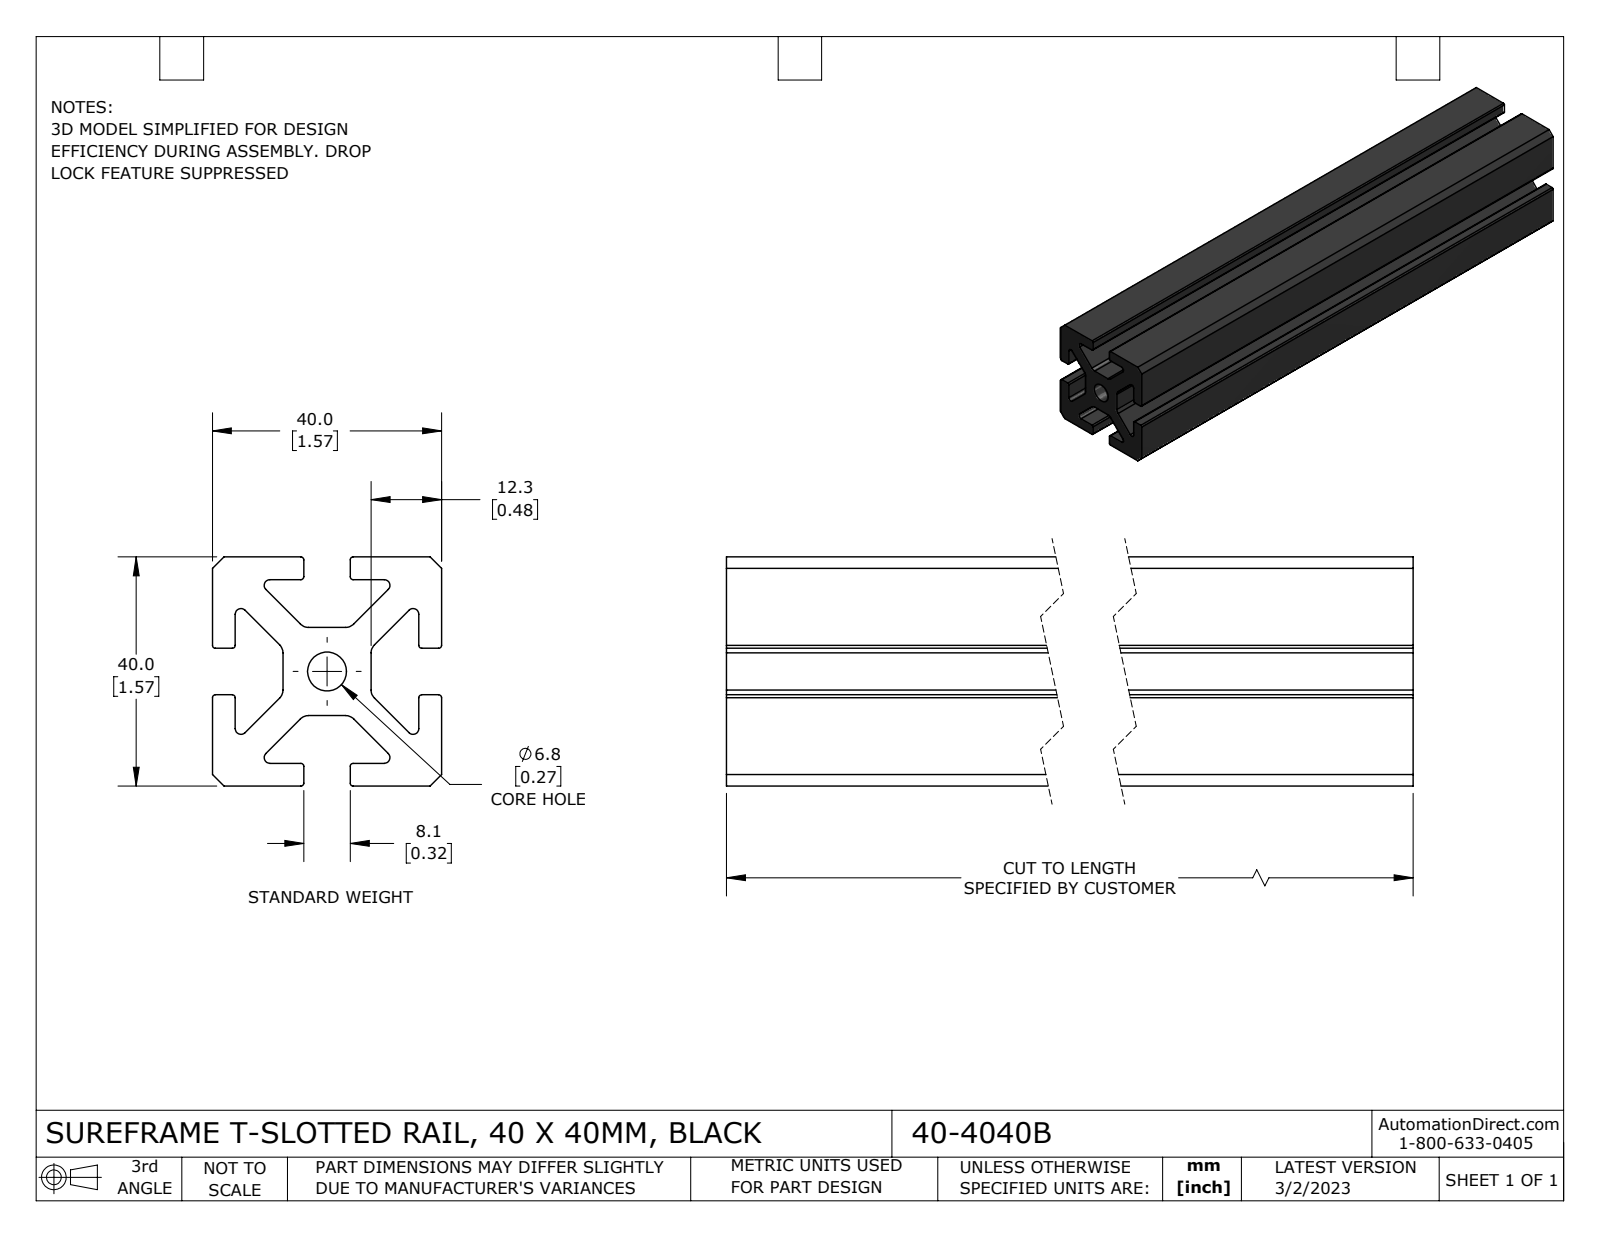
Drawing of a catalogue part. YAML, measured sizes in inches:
part_name: "40-4040B"
step_written_by: "SolidWorks 2021 (CONFIG_CONTROL_DESIGN)"
units: inches
bodies: {solids: 1, faces: 78, planar: 42, cylindrical: 36, other: 0}
overall_size: [8, 1.575, 1.575]
volume: 11
surface_area: 111.5
round_holes:
  - {diameter: 0.268, count: 1}
partial_cylinders:
  - {radius: 0.02, count: 16}
  - {radius: 0.039, count: 8}
  - {radius: 0.079, count: 8}
face_to_face_distances: [1.575, 0.156, 1.419, 0.202, 0.484, 1.091, 0.328, 0.934, 0.628, 0.947]
